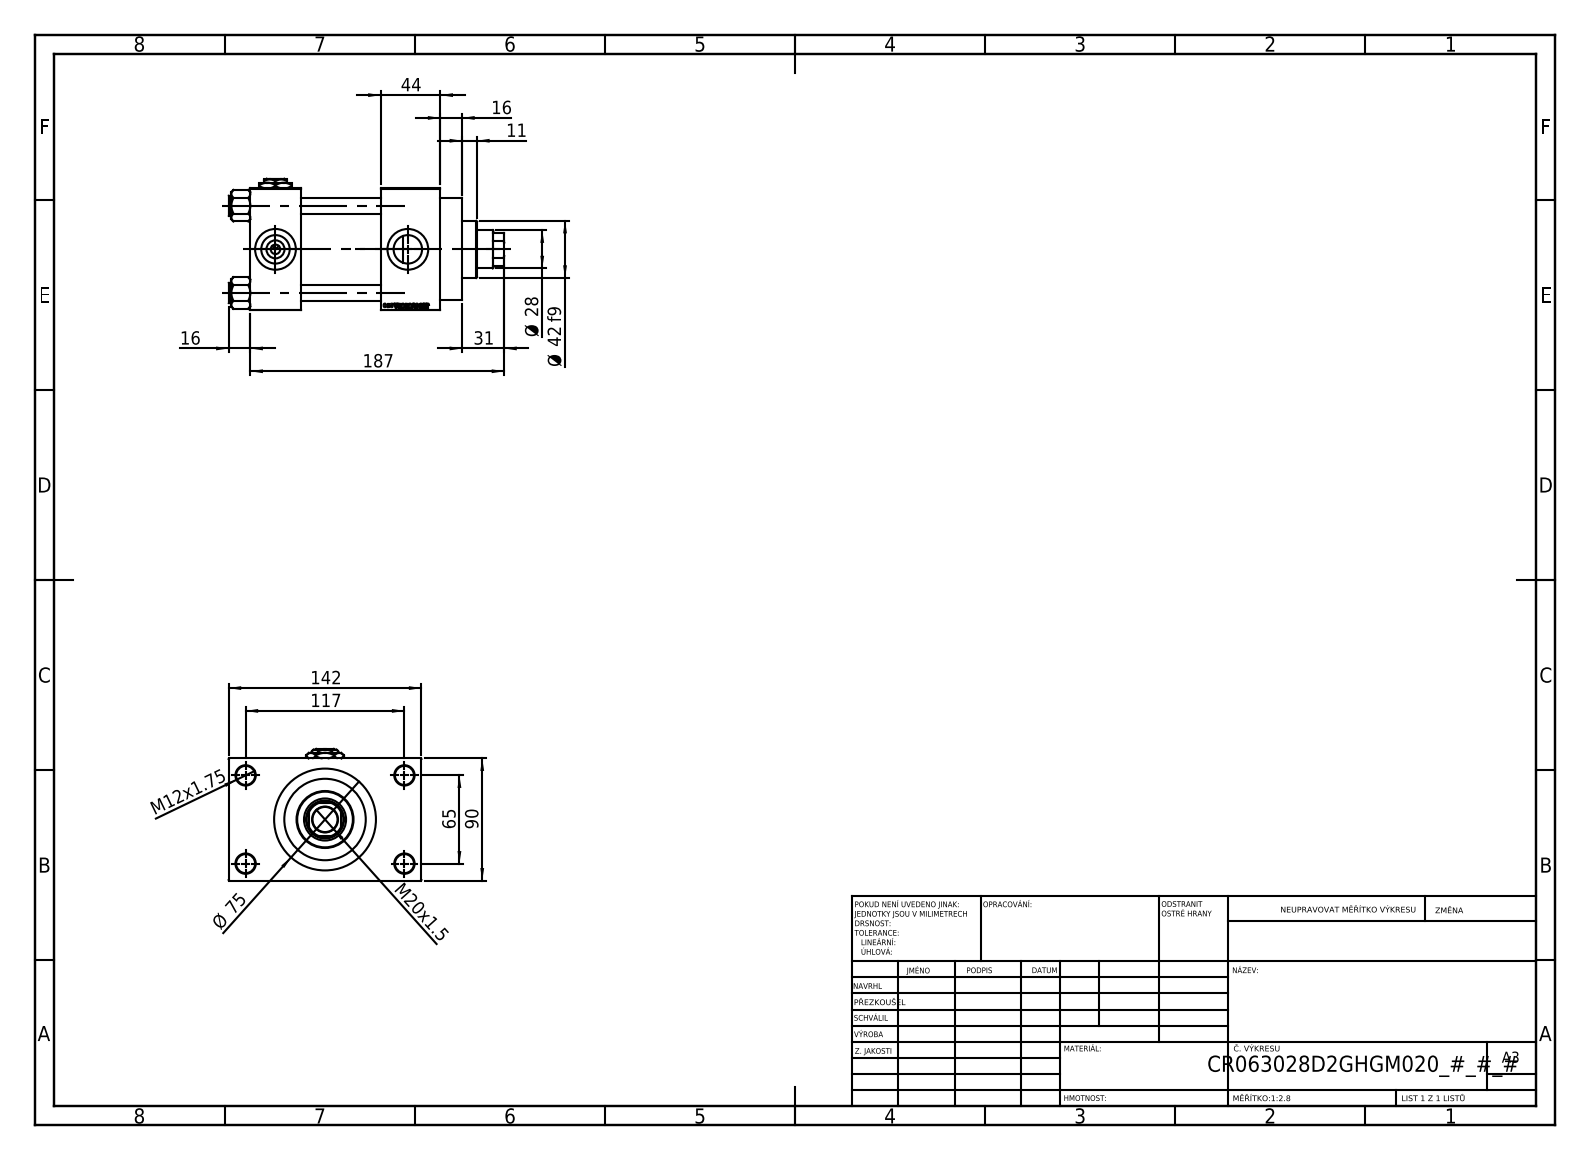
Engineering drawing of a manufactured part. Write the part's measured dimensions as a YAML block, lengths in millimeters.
part_name: "NUT_M5_D; V215CR_D_Body; V215CR_D_TYCINKA; V215_VC_A (+2 more)"
step_written_by: "SolidWorks 2019 (CONFIG_CONTROL_DESIGN)"
units: millimeters
bodies: {solids: 12, faces: 1156, planar: 521, cylindrical: 95, other: 540}
overall_size: [203, 142, 97]
volume: 1094000
surface_area: 203085
round_holes:
  - {diameter: 12, count: 4}
  - {diameter: 14, count: 4}
  - {diameter: 7, count: 3}
  - {diameter: 20.96, count: 3}
  - {diameter: 30, count: 3}
  - {diameter: 18.5, count: 1}
  - {diameter: 28, count: 1}
  - {diameter: 31, count: 1}
  - {diameter: 50, count: 1}
  - {diameter: 60, count: 1}
  - {diameter: 63, count: 1}
round_bosses_or_shafts:
  - {diameter: 15, count: 4}
  - {diameter: 75, count: 1}
  - {diameter: 69, count: 1}
  - {diameter: 42, count: 1}
partial_cylinders:
  - {radius: 13.5, count: 1}
face_to_face_distances: [90, 59, 37, 96, 140, 103, 44, 26, 116, 16]
hole_center_spacings: [26.35, 45.47, 64.3, 66.92, 69.81, 90.65, 111.34, 65]
